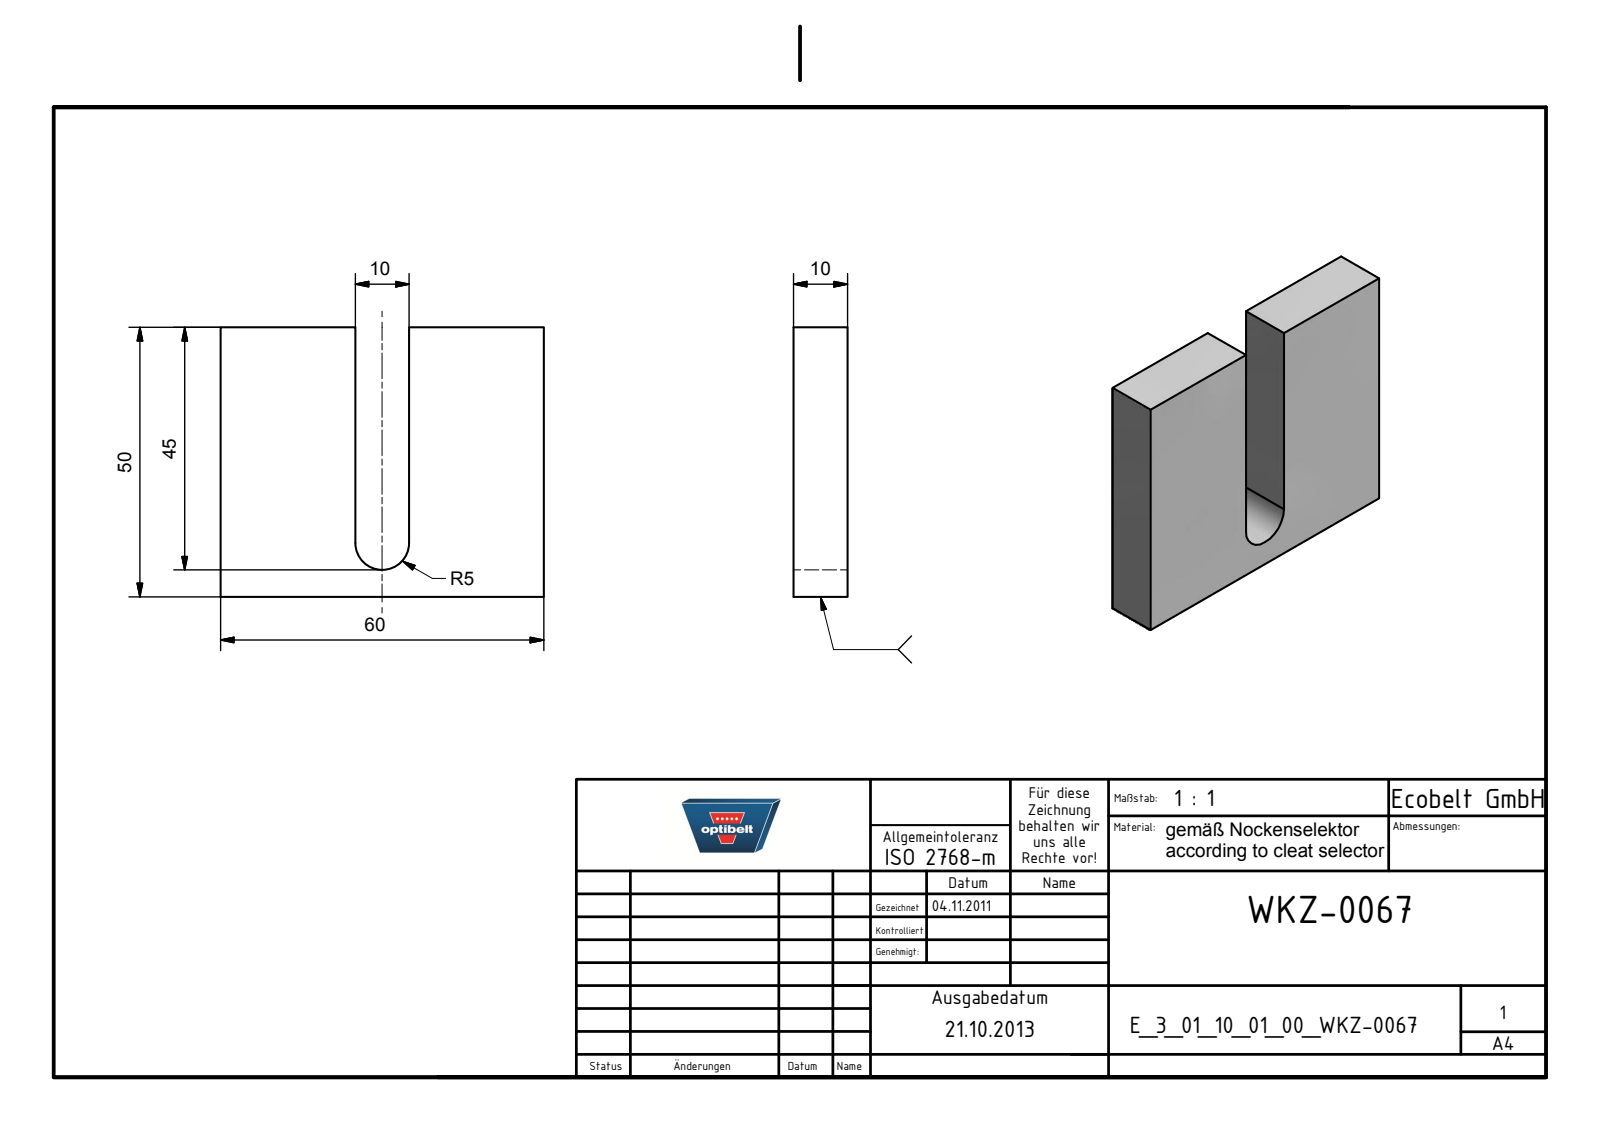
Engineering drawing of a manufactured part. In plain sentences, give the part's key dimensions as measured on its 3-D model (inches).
The part is named "E_3_01_10_01_00_WKZ-0067". Its 3-D file was written by "Autodesk Inventor 2025 (AUTOMOTIVE_DESIGN)". It is 1 solid with 10 faces: 9 planar, 1 cylindrical and 0 other. Overall it measures 2.362 by 1.969 by 0.394 inches. Its volume is 1.563 cubic inches and its surface area 12.68 square inches. Partial cylindrical surfaces (rounded edges, fillets, slot ends): 1 of radius 0.197. The main face-to-face distances are 0.394, 0.984, 1.378, 2.362, 1.969.
